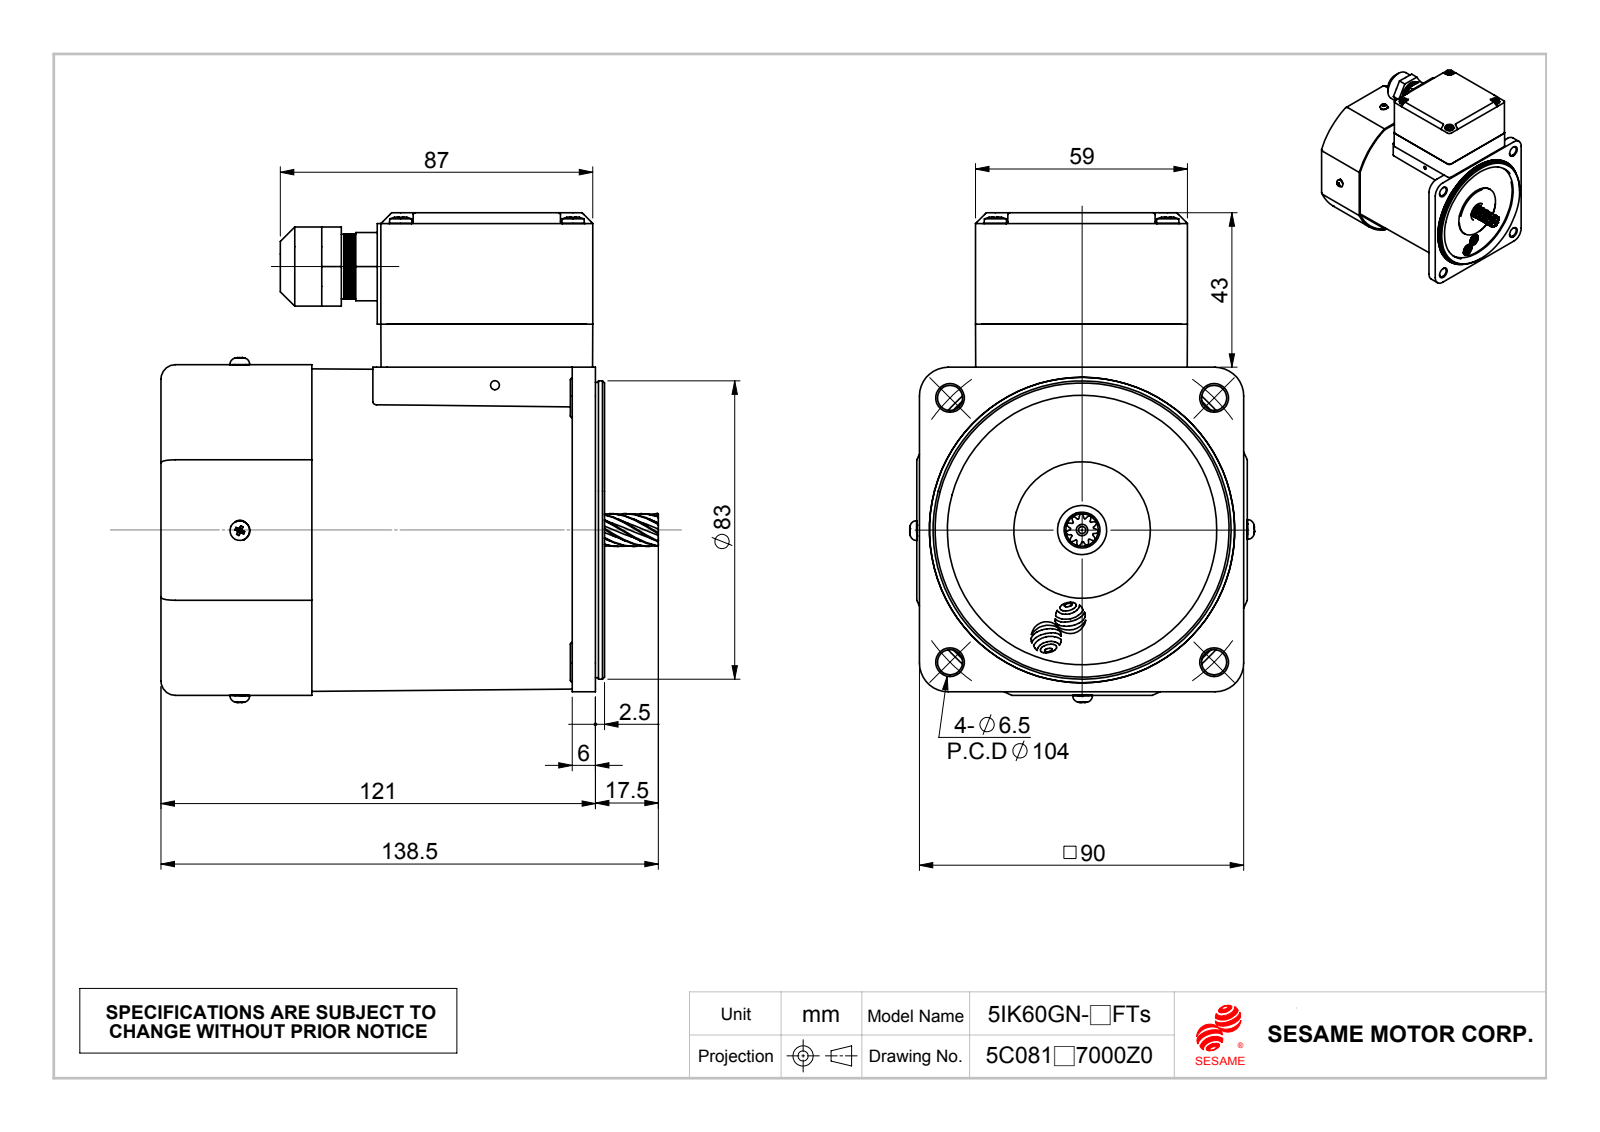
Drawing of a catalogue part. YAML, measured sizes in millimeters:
part_name: "成品180度; M560Ts-F; 風扇蓋FC-9042-21; 60GN (+1 more)"
step_written_by: "SolidWorks 2010 (CONFIG_CONTROL_DESIGN)"
units: millimeters
bodies: {solids: 16, faces: 2886, planar: 343, cylindrical: 1076, other: 1467}
overall_size: [138.5, 136.29, 95.99]
volume: 846885
surface_area: 135764
round_holes:
  - {diameter: 2.5, count: 5}
  - {diameter: 3.3, count: 4}
  - {diameter: 3.5, count: 4}
  - {diameter: 3.9, count: 4}
  - {diameter: 4.3, count: 4}
  - {diameter: 7, count: 4}
  - {diameter: 2, count: 1}
  - {diameter: 6.5, count: 1}
  - {diameter: 11, count: 1}
  - {diameter: 12, count: 1}
  - {diameter: 13.7, count: 1}
  - {diameter: 14.5, count: 1}
round_bosses_or_shafts:
  - {diameter: 3, count: 8}
  - {diameter: 6.3, count: 4}
  - {diameter: 5.5, count: 4}
  - {diameter: 85, count: 1}
  - {diameter: 84.22, count: 1}
  - {diameter: 83, count: 1}
  - {diameter: 82.2, count: 1}
  - {diameter: 47, count: 1}
partial_cylinders:
  - {radius: 0.3, count: 16}
  - {radius: 2, count: 16}
  - {radius: 1, count: 10}
  - {radius: 4, count: 10}
  - {radius: 0.5, count: 8}
  - {radius: 0.78, count: 8}
  - {radius: 1.5, count: 8}
  - {radius: 1.66, count: 8}
face_to_face_distances: [1, 118.5, 12, 91, 102.5, 16, 118.4, 119.4, 117.5, 0.9]
hole_center_spacings: [48, 52, 73.54, 11.67, 12.35, 12.7, 24.93, 25]
